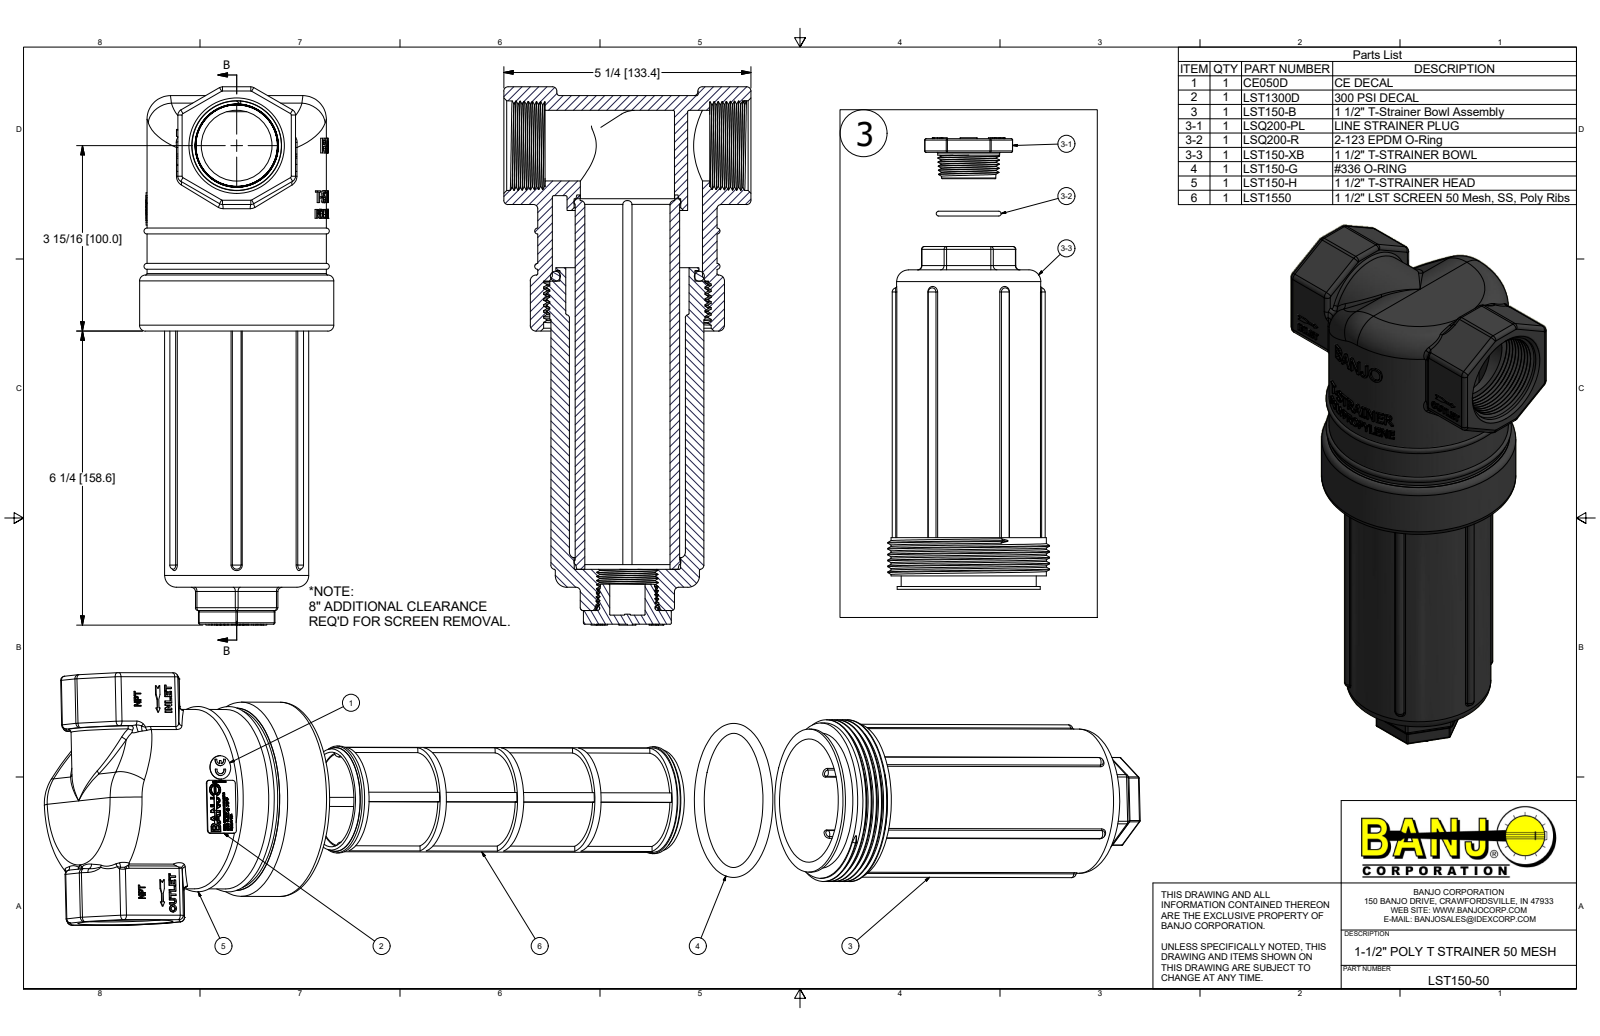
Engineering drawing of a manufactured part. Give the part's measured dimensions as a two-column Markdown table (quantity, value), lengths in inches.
| quantity | value |
| --- | --- |
| part name | LST150-50; CE050D; LST1300D; LST150-B (+6 more) |
| STEP written by | Autodesk Inventor 2018 (AUTOMOTIVE_DESIGN) |
| units | inches |
| bodies | 8 solids, 3120 faces (1691 planar, 290 cylindrical, 1139 other) |
| overall size | 11.433 × 5.25 × 4.125 |
| volume | 49.55 in³ |
| surface area | 482.1 in² |
| round holes (diameter × count) | 0.181 × 1, 0.257 × 1, 0.75 × 1, 1.5 × 1, 1.81 × 1, 1.97 × 1, 2 × 1, 2.26 × 1, 2.265 × 1, 2.62 × 1, 3.19 × 1, 3.425 × 1 |
| round bosses / shafts (diameter × count) | 4.125 × 1, 3.81 × 1, 3.435 × 1, 3.3 × 1, 3.063 × 1, 3.04 × 1, 2.87 × 1, 2.563 × 1 |
| partial cylindrical surfaces (radius × count) | 0.03 × 44, 0.09 × 34, 0.06 × 16, 0.125 × 10, 0.078 × 6, 0.094 × 6, 0.1 × 4, 0.026 × 2 |
| main face-to-face distances | 2.5, 6.12, 10.06, 3.94, 0.92, 1.24, 9.748, 3.628, 0.313, 1.85 |
